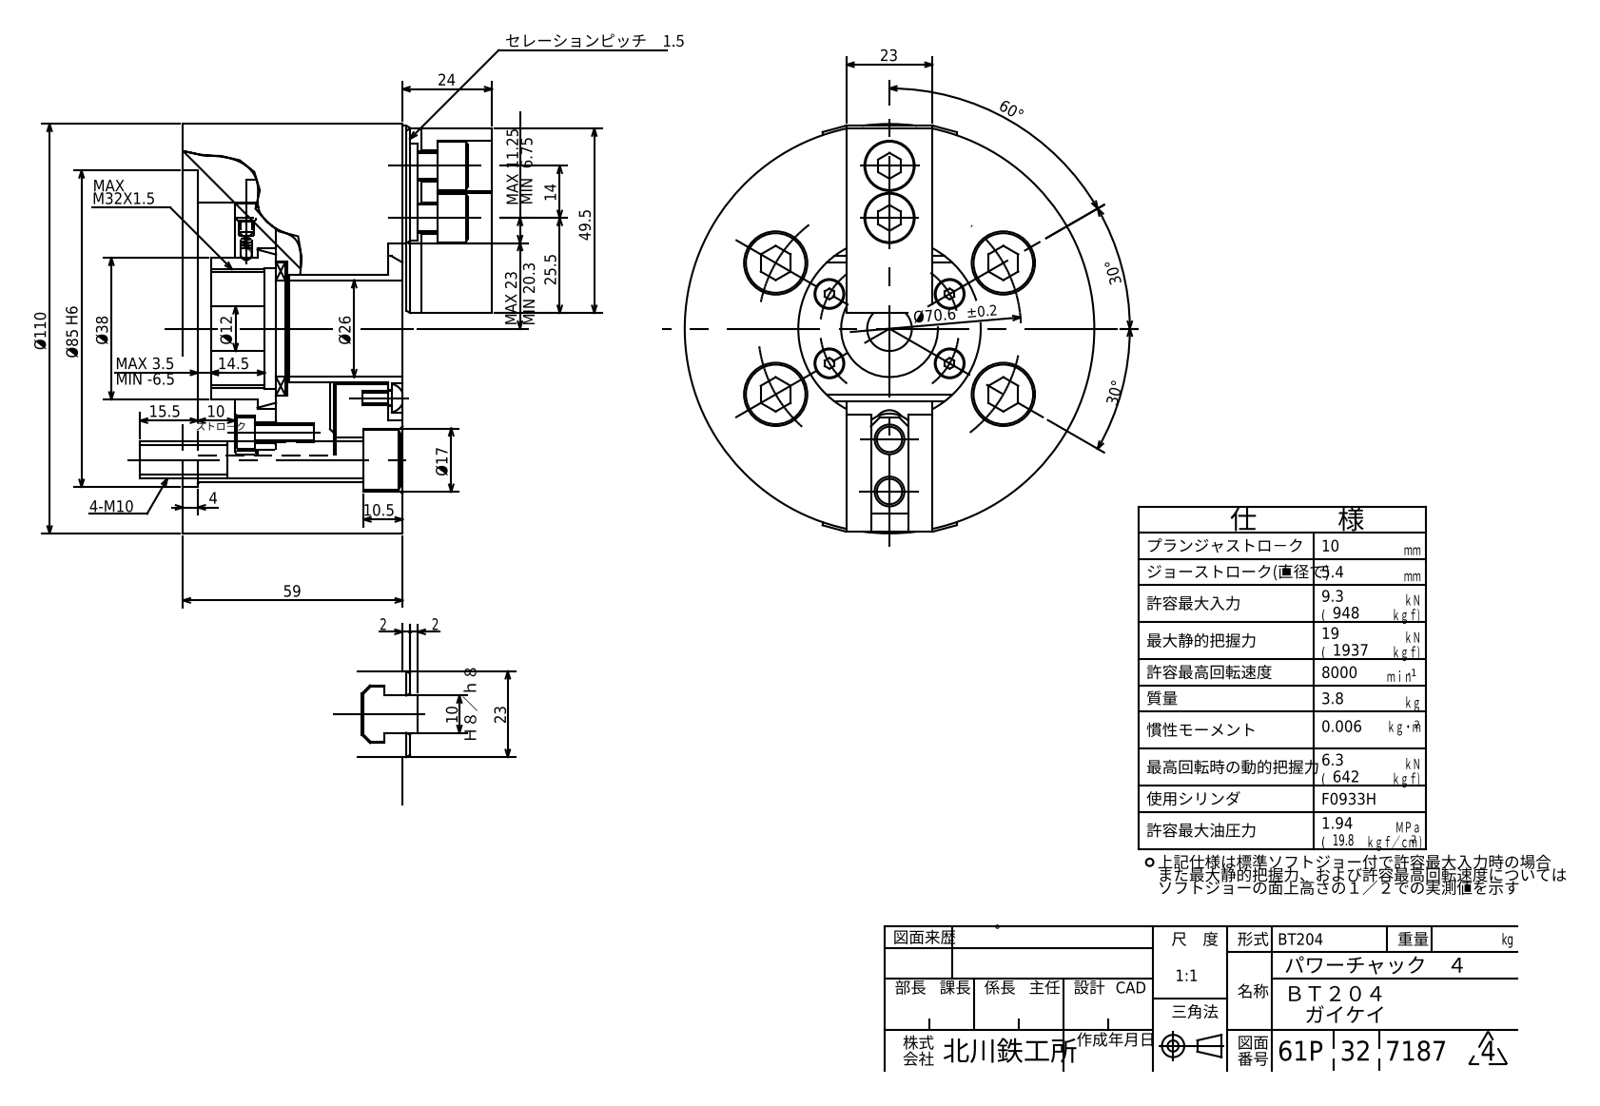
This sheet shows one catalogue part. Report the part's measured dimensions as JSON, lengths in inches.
{"part_name": "BT204 CHUCK", "step_written_by": "ST-DEVELOPER v16.7 (AUTOMOTIVE_DESIGN)", "units": "inches", "bodies": {"solids": 3, "faces": 194, "planar": 113, "cylindrical": 28, "other": 53}, "overall_size": [4.331, 4.331, 3.268], "volume_in3": 27.08, "surface_area_in2": 103.1, "round_holes": [[0.128, 4], [0.335, 4], [0.394, 4], [0.531, 4], [0.669, 4], [1.142, 1], [1.929, 1], [2.677, 1], [3.346, 1]], "round_bosses_or_shafts": [[4.331, 1]], "face_to_face_distances": [2.165, 1.102, 0.906, 2.323, 0.945, 0.157, 1.22, 2.362, 0.039, 1.26], "hole_center_spacings": [0.728, 1.39, 0.661, 1.001, 1.204, 1.284, 1.471, 1.563]}
